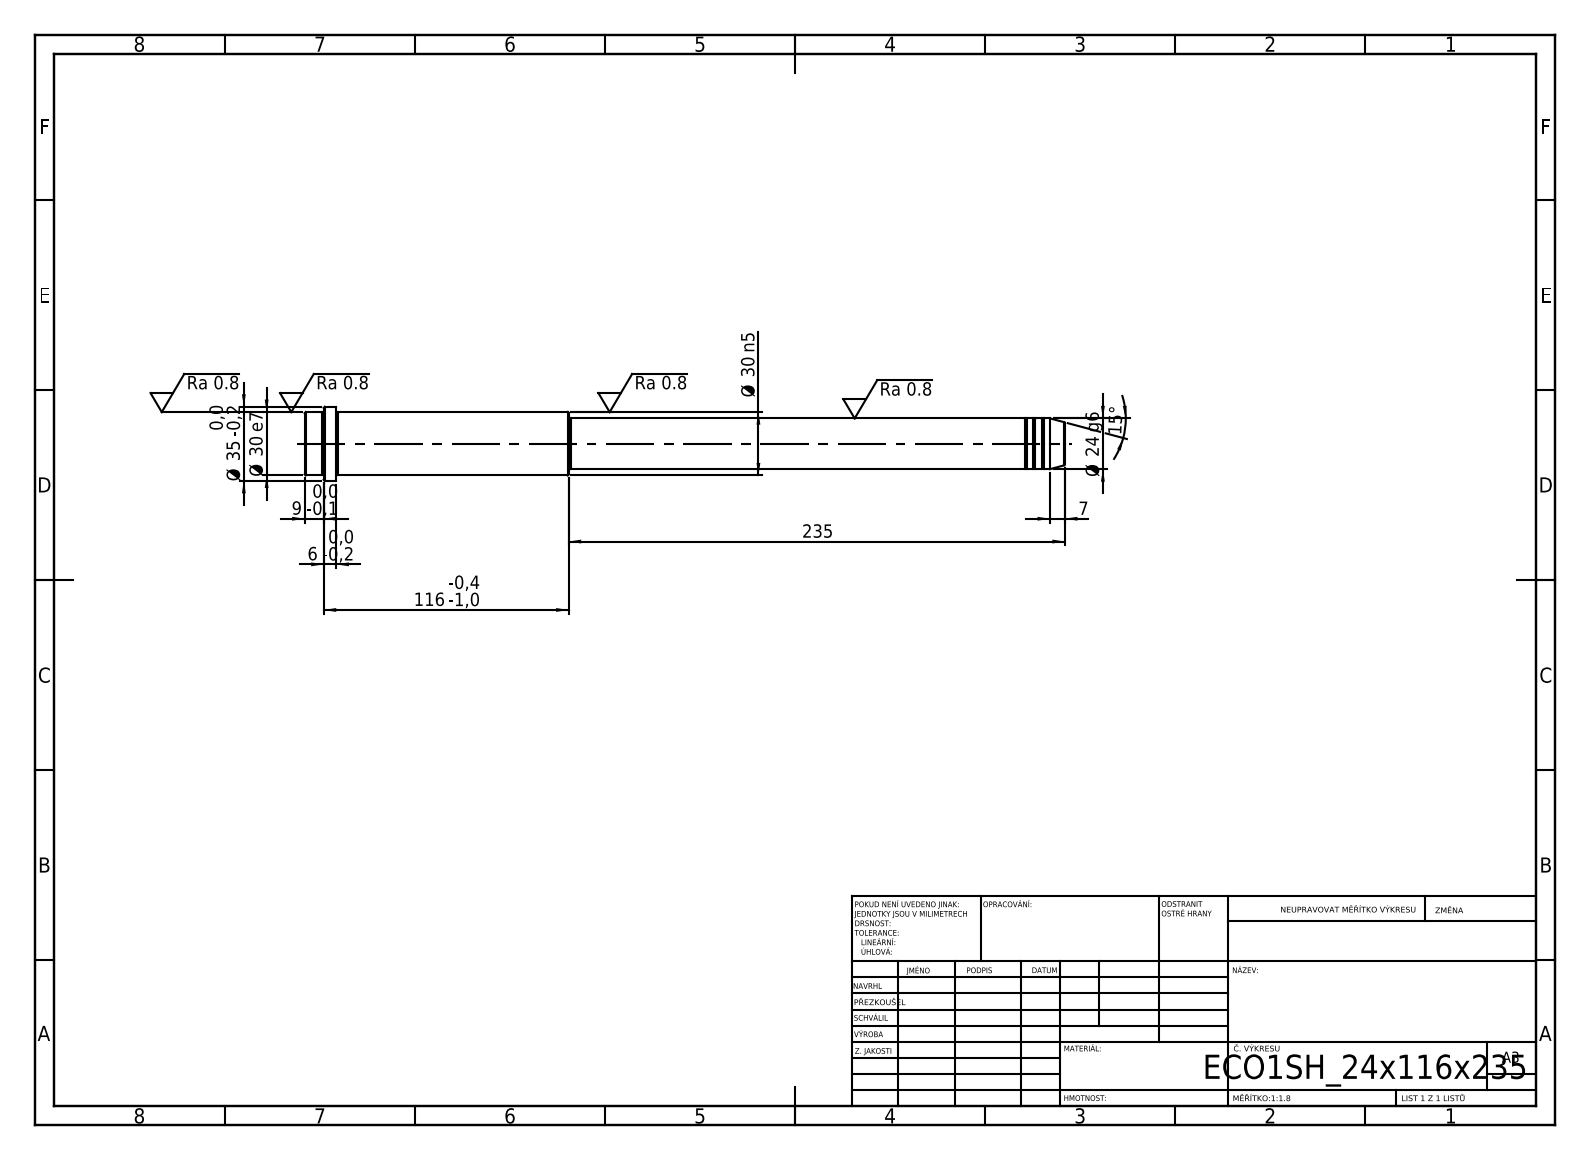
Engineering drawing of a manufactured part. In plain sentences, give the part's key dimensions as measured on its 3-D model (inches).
Its 3-D file was written by "SolidWorks 2019 (CONFIG_CONTROL_DESIGN)". It is 1 solid with 52 faces: 6 planar, 16 cylindrical and 30 other. Overall it measures 14.173 by 1.378 by 1.378 inches. Its volume is 11.93 cubic inches and its surface area 48.92 square inches. Round bosses or shafts: 1 of diameter 1.378, 1 of diameter 1.181, 1 of diameter 0.945, 1 of diameter 0.906. The main face-to-face distances are 14.173, 13.583, 0.591, 9.252, 4.331, 4.921, 13.819, 4.567, 0.236, 0.354.
